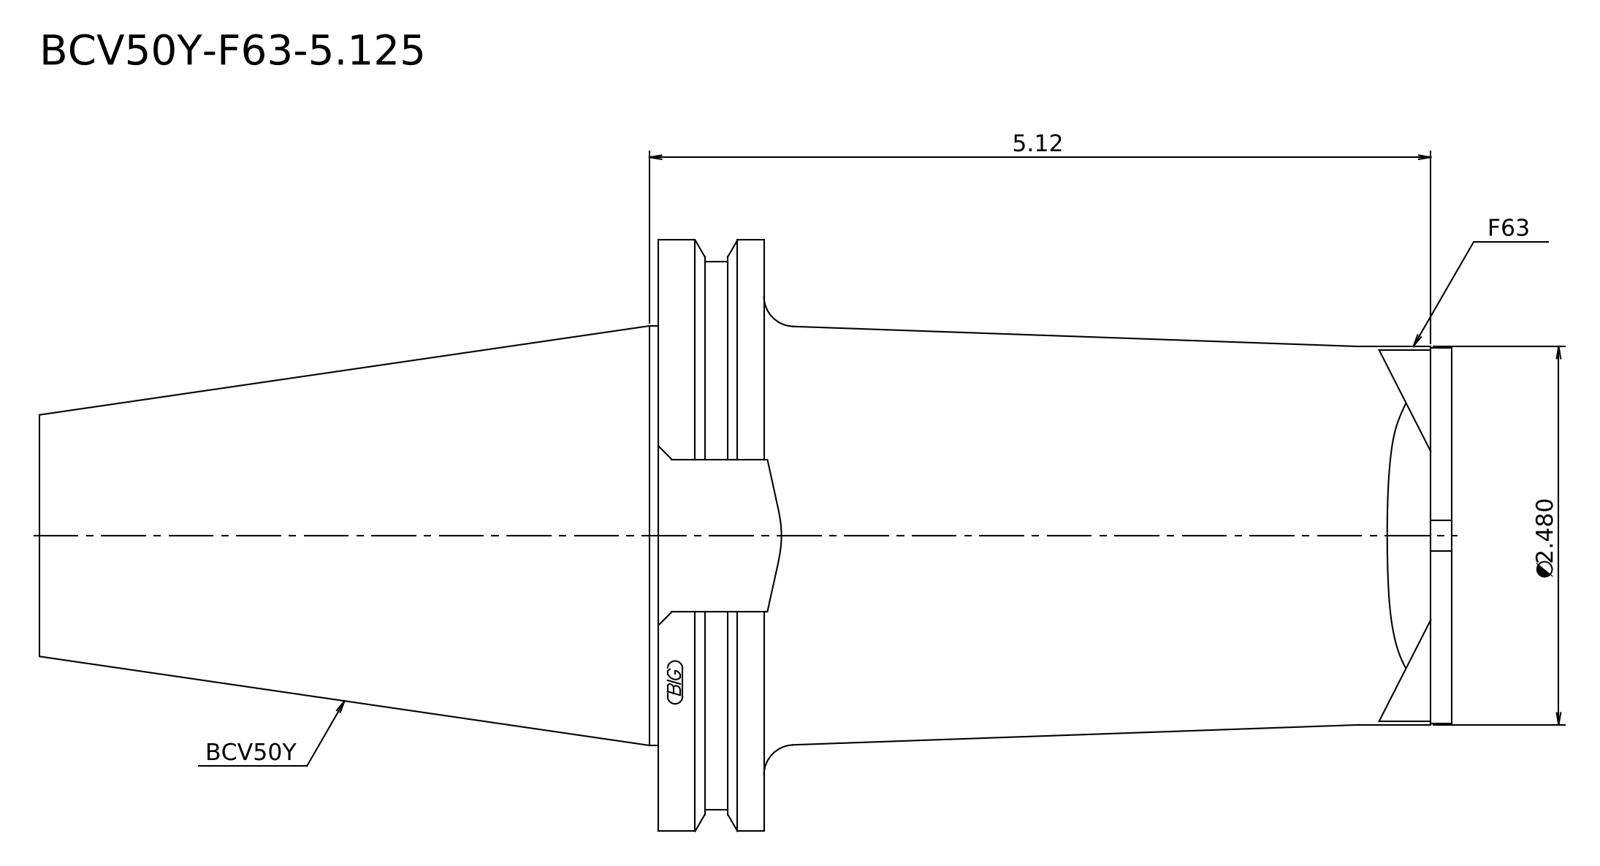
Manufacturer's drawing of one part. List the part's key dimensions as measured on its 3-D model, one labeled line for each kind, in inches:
STEP written by: Kubotek KeyCreator 2011 V10.0.2 (22737) (automotive_design)
Units: inches
Bodies: 1 solid, 16 faces (6 planar, 5 cylindrical, 5 other)
Overall size (bounding box): 9.122 × 3.875 × 3.875
Volume: 46.73 in³ · Surface area: 91.84 in²
Round bosses / shafts (diameter × count): ⌀3.875 ×1, ⌀3.594 ×1, ⌀2.75 ×1, ⌀2.48 ×1
Main face-to-face distances: 5.063, 4.372, 0.691, 9.122, 4.75, 4.059, 4.76, 0.388, 0.303, 4.362
